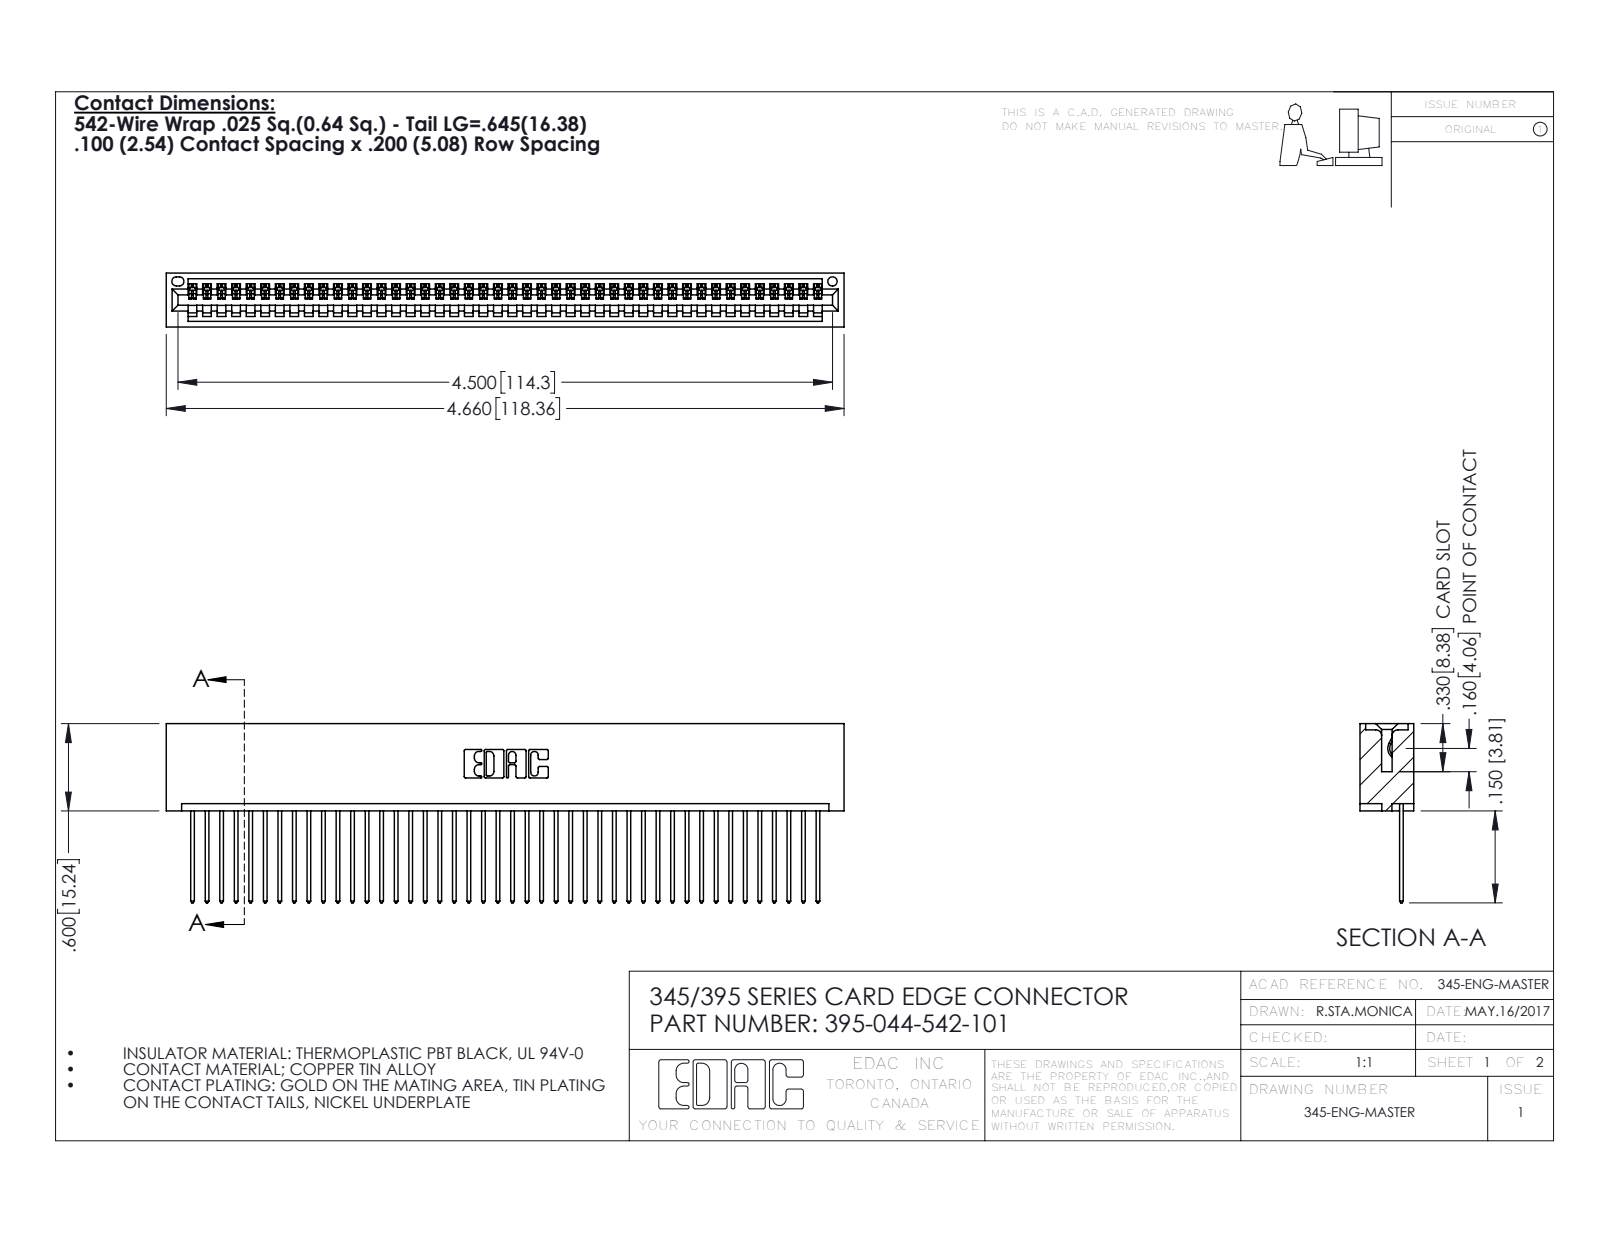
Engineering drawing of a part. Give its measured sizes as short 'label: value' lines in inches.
name: 395-044-542-101; 345-292-001_345-293-142; 345 Part_No Mounting Lugs
written by: SolidWorks 2016 (CONFIG_CONTROL_DESIGN)
unit: in
bodies: 45 solids, 2670 faces (1836 planar, 834 cylindrical, 0 other)
size: 4.66 × 1.232 × 0.37
volume: 0.729 in³; area: 25.89 in²
holes: 1× ⌀0.064
rounds: 88× R0.006, 88× R0.01, 22× R0.01, 6× R0.007, 6× R0.031, 3× R0.026, 2× R0.031, 2× R0.04
face distances: 0.072, 0.298, 0.098, 0.272, 0.025, 0.37, 0.2, 0.225, 0.149, 0.072
